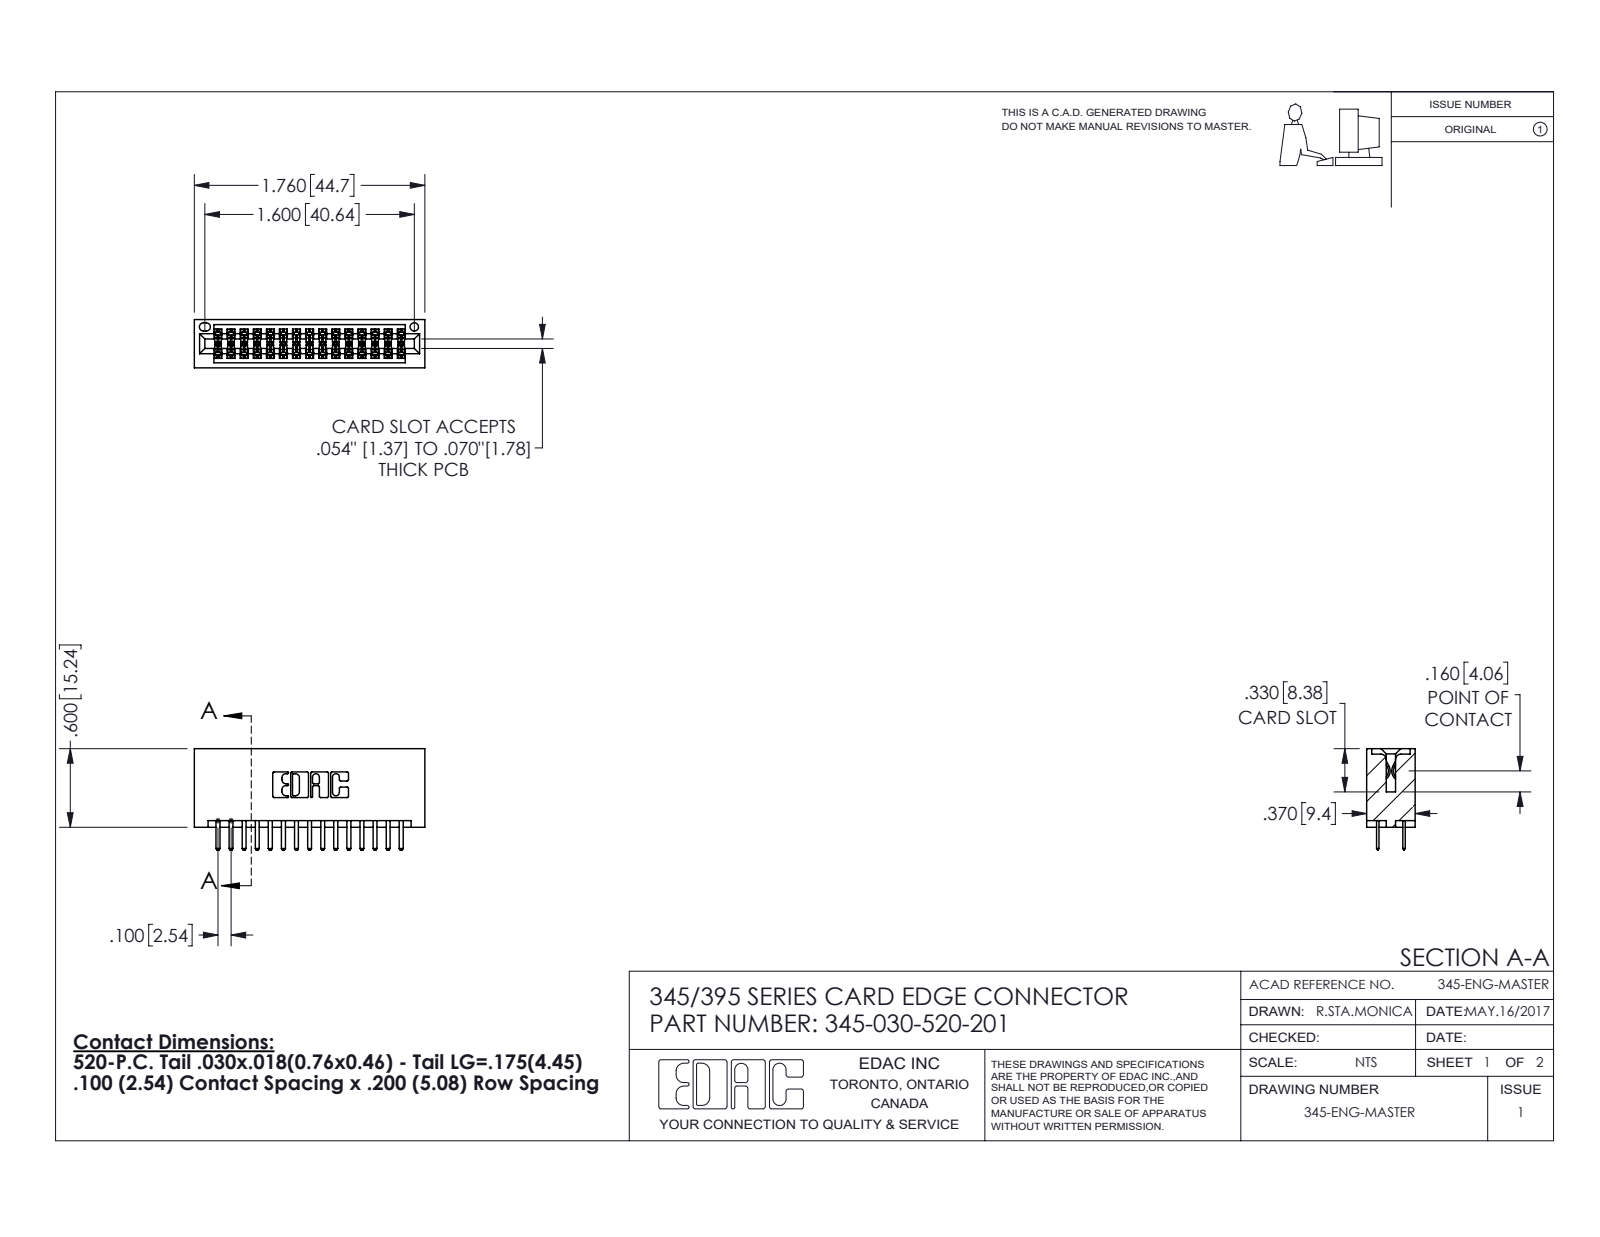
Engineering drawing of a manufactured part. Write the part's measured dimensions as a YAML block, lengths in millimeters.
part_name: "345-030-520-201; 345-292-001_345-293-120; 345 Part_No Mounting Lugs"
step_written_by: "SolidWorks 2016 (CONFIG_CONTROL_DESIGN)"
units: millimeters
bodies: {solids: 31, faces: 1738, planar: 1126, cylindrical: 612, other: 0}
overall_size: [44.7, 19.7, 9.4]
volume: 4690
surface_area: 6690
round_holes:
  - {diameter: 1.6, count: 1}
partial_cylinders:
  - {radius: 0.2, count: 45}
  - {radius: 0.3, count: 34}
  - {radius: 0.3, count: 22}
  - {radius: 0.2, count: 6}
  - {radius: 0.8, count: 6}
  - {radius: 0.7, count: 3}
  - {radius: 0.4, count: 2}
  - {radius: 0.5, count: 2}
face_to_face_distances: [5.1, 7.6, 1.8, 9.4, 2.5, 6.9, 0.6, 5.7, 2.5, 7.6]
